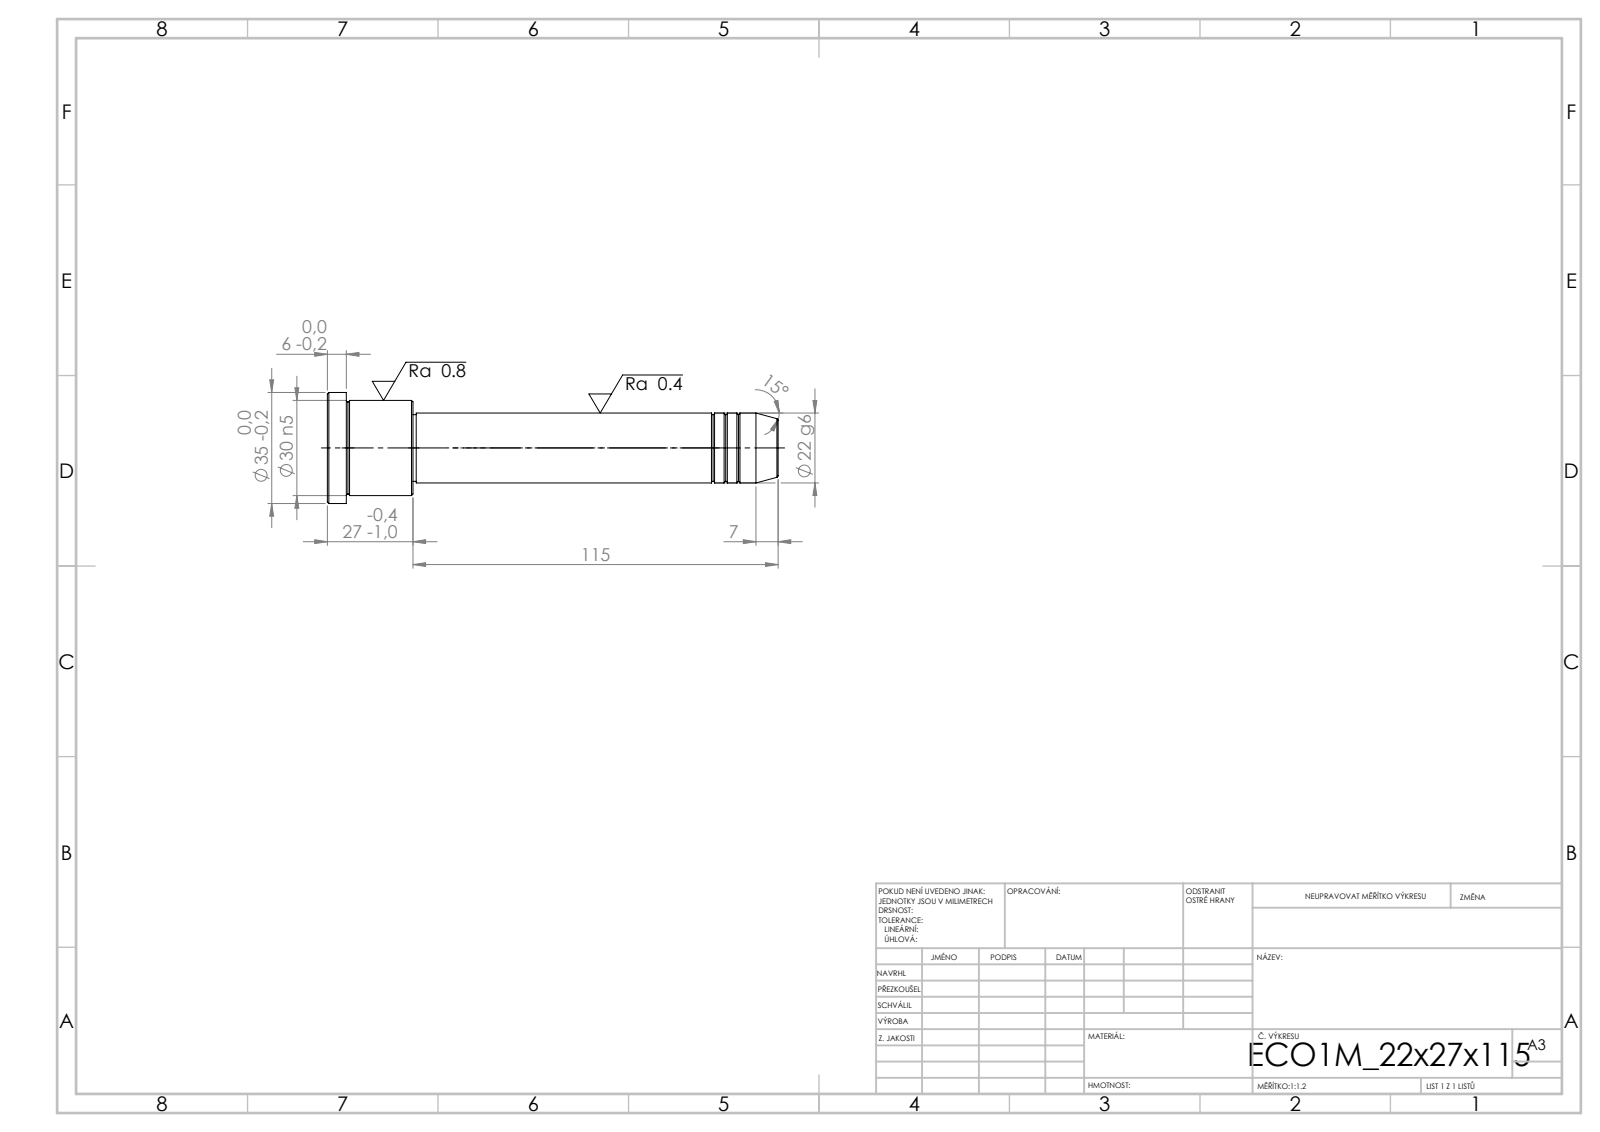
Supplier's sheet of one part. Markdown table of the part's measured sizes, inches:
| quantity | value |
| --- | --- |
| STEP written by | SolidWorks 2019 (CONFIG_CONTROL_DESIGN) |
| units | inches |
| bodies | 1 solid, 43 faces (5 planar, 14 cylindrical, 24 other) |
| overall size | 5.591 × 1.378 × 1.378 |
| volume | 3.889 in³ |
| surface area | 19.41 in² |
| round bosses / shafts (diameter × count) | 1.378 × 1, 1.181 × 1, 0.866 × 1, 0.827 × 1 |
| main face-to-face distances | 1.063, 0.827, 0.236, 4.528, 5.354, 5.591, 4.488, 0.039, 0.866, 1.102 |
